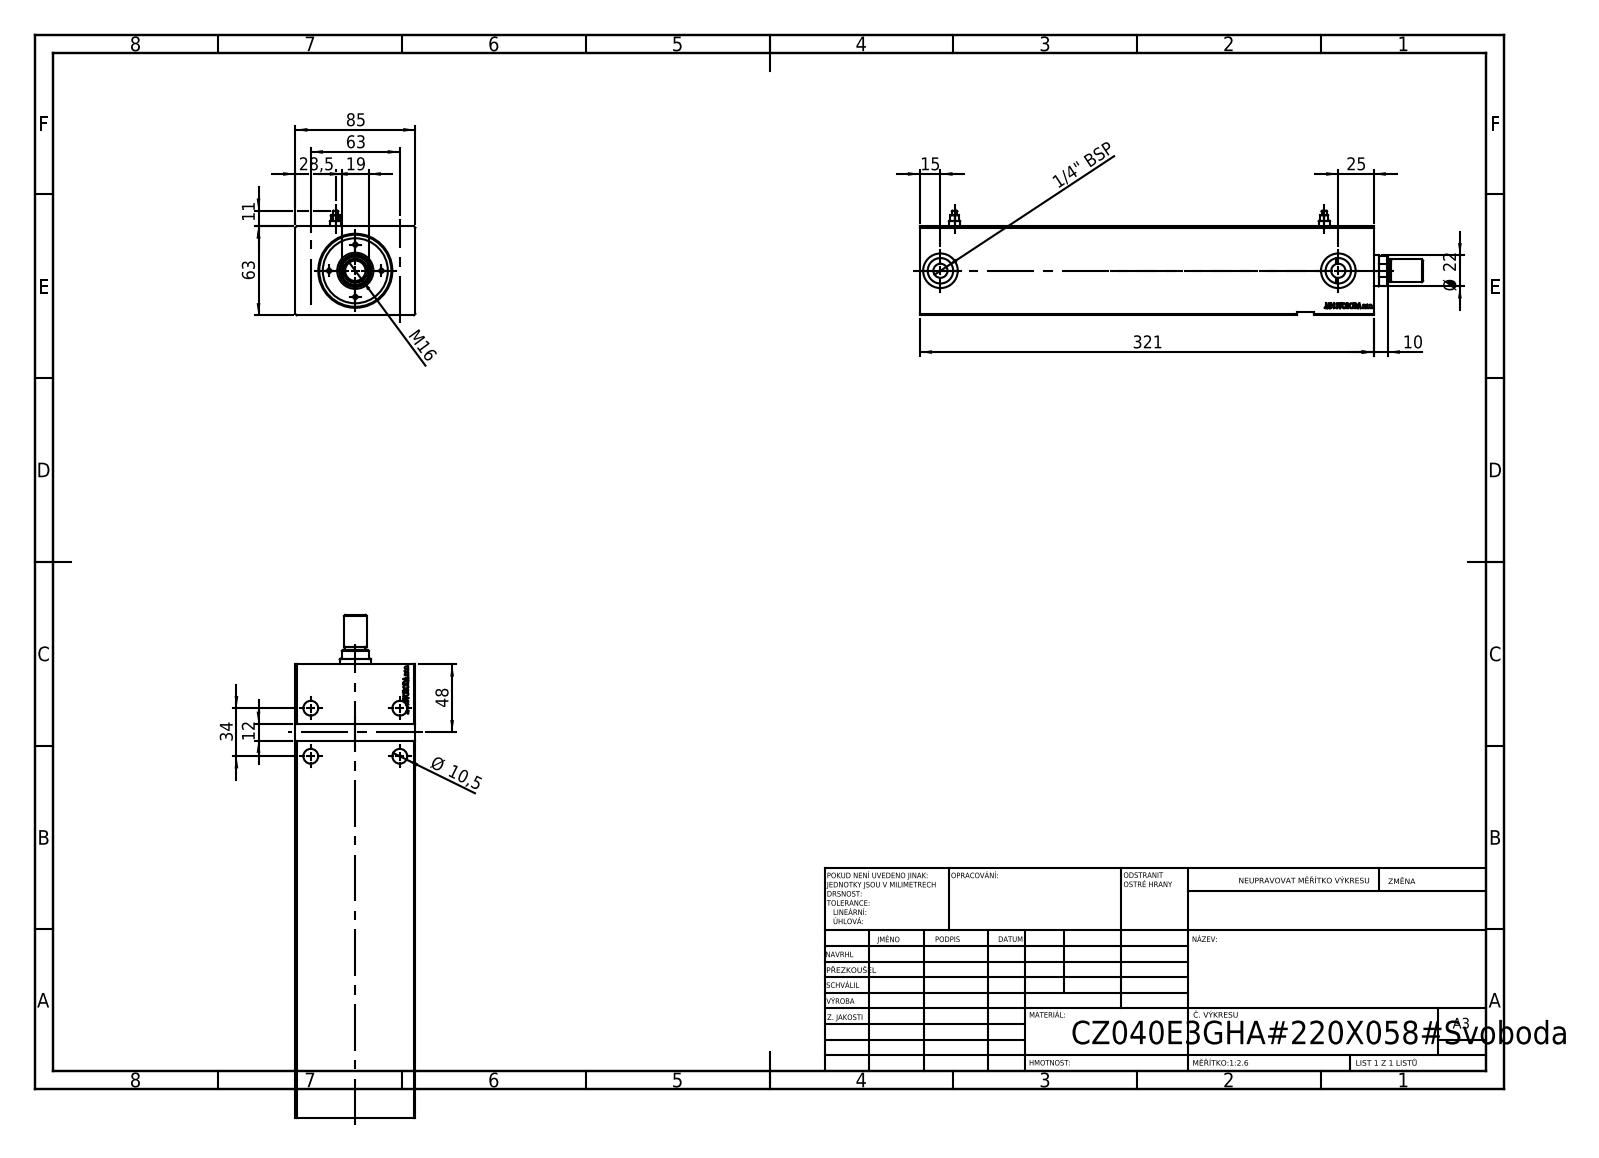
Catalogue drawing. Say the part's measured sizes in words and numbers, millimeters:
Its 3-D file was written by "SolidWorks 2019 (CONFIG_CONTROL_DESIGN)". It is 1 solid with 797 faces: 383 planar, 30 cylindrical and 384 other. Overall it measures 321 by 85 by 63 millimeters. Its volume is 1 295 000 cubic millimeters and its surface area 153 268 square millimeters. Round holes: 4 of diameter 10.5, 2 of diameter 8, 2 of diameter 10, 2 of diameter 18, 2 of diameter 24.5, 1 of diameter 36, 1 of diameter 40, 1 of diameter 51. The main face-to-face distances are 63, 85, 321, 305.7, 15.3, 2, 61, 320.8, 15.1, 103.22. The hole center spacings are 34, 63, 71.59, 17.95, 34.73, 45.68, 54.5, 232.16.
